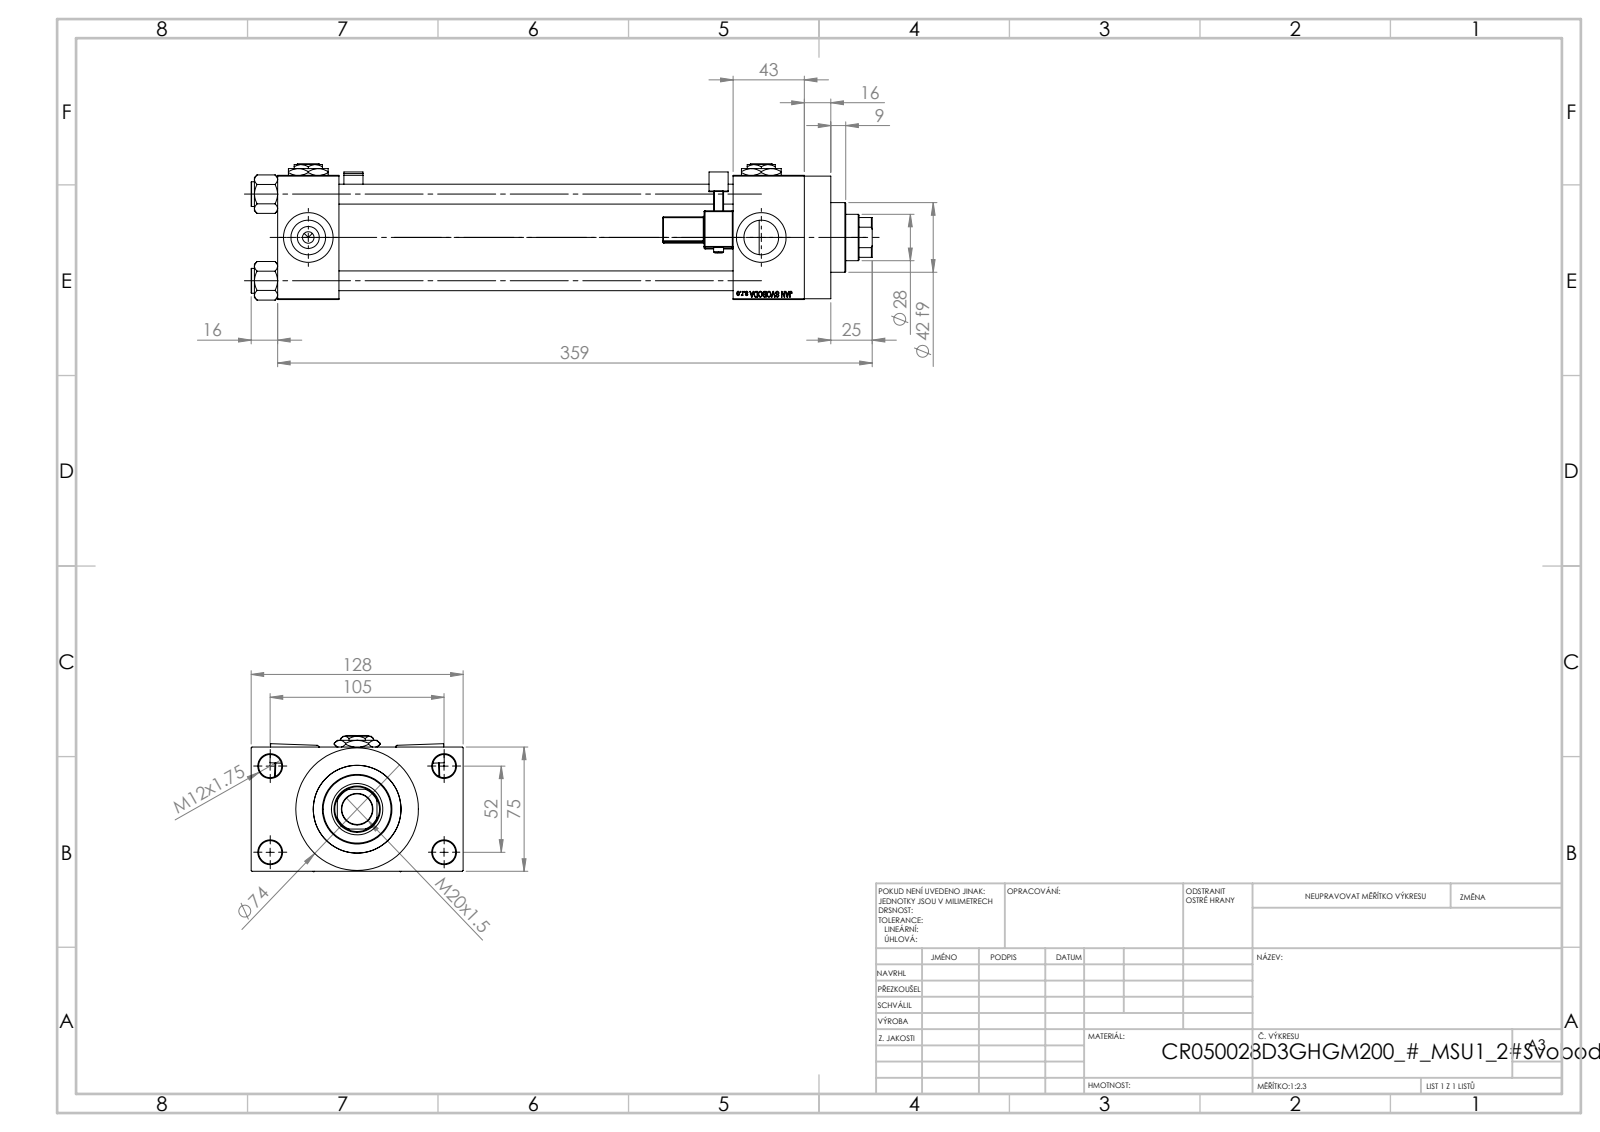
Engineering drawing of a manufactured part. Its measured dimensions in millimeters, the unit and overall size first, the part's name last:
Units: millimetres
Overall size (bounding box): 375 × 128 × 82.27
Round holes (diameter × count): ⌀12 ×4, ⌀14 ×4, ⌀20.96 ×4, ⌀30 ×4, ⌀7 ×3, ⌀18.5 ×1, ⌀28 ×1, ⌀31 ×1, ⌀41 ×1, ⌀50 ×1, ⌀53 ×1
Round bosses / shafts (diameter × count): ⌀15 ×4, ⌀6 ×2, ⌀74 ×1, ⌀56 ×1, ⌀42 ×1
Partial cylindrical surfaces — rounded edges, fillets, slot ends (radius × count): R0.5 ×48, R1 ×2, R2.5 ×2, R4 ×2, R13.5 ×1
Main face-to-face distances: 75, 238, 37, 275, 26.5, 101.5, 318, 281, 43, 16
Hole centre spacings: 26.35, 36.98, 52.3, 58.43, 58.59, 78.65, 94.37, 52
Volume: 1 125 000 mm³ · Surface area: 290 030 mm²
Bodies: 15 solids, 1358 faces (603 planar, 159 cylindrical, 596 other)
Part name (STEP PRODUCT): V215CR_D_TYCINKA; V215CR_D_Body; V215_VC_A; V215CR_VCP_D (+3 more)
STEP written by: SolidWorks 2019 (CONFIG_CONTROL_DESIGN)
